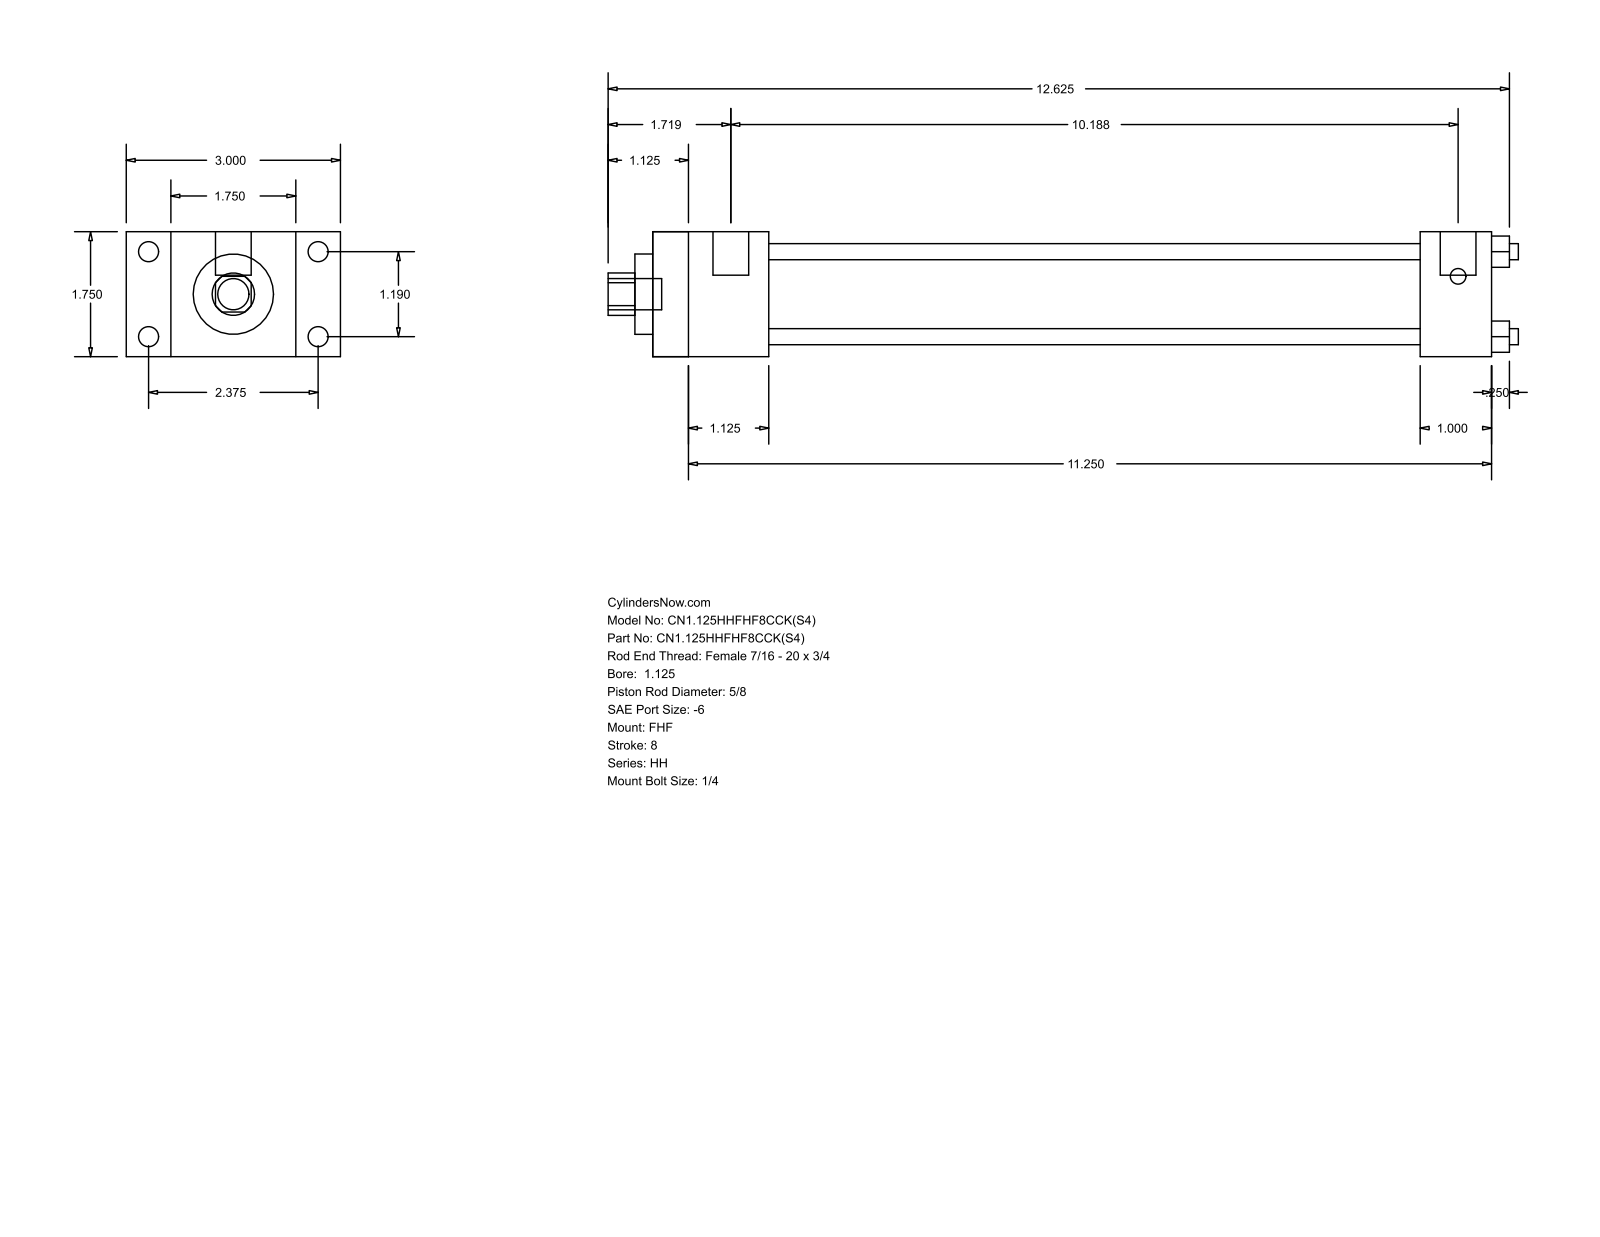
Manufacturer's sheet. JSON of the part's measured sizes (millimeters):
{"part_name": "HH_FHF__0112_0.625", "step_written_by": "GSSL Pune (CONFIG_CONTROL_DESIGN)", "units": "millimeters", "bodies": {"solids": 0, "faces": 88, "planar": 60, "cylindrical": 28, "other": 0}, "overall_size": [323.85, 76.2, 44.45], "round_holes": [[5.71, 4], [15.88, 1], [28.57, 1], [34.92, 1]], "round_bosses_or_shafts": [[7.14, 4], [5.56, 4], [12.7, 2], [11.11, 1]], "partial_cylinders_radius": [[7.54, 1]], "face_to_face_distances": [44.46, 15.87, 60.33, 41.27, 76.2, 298.44, 257.17, 273.05, 231.78, 25.39], "hole_center_spacings": [21.37, 30.22, 42.74]}
